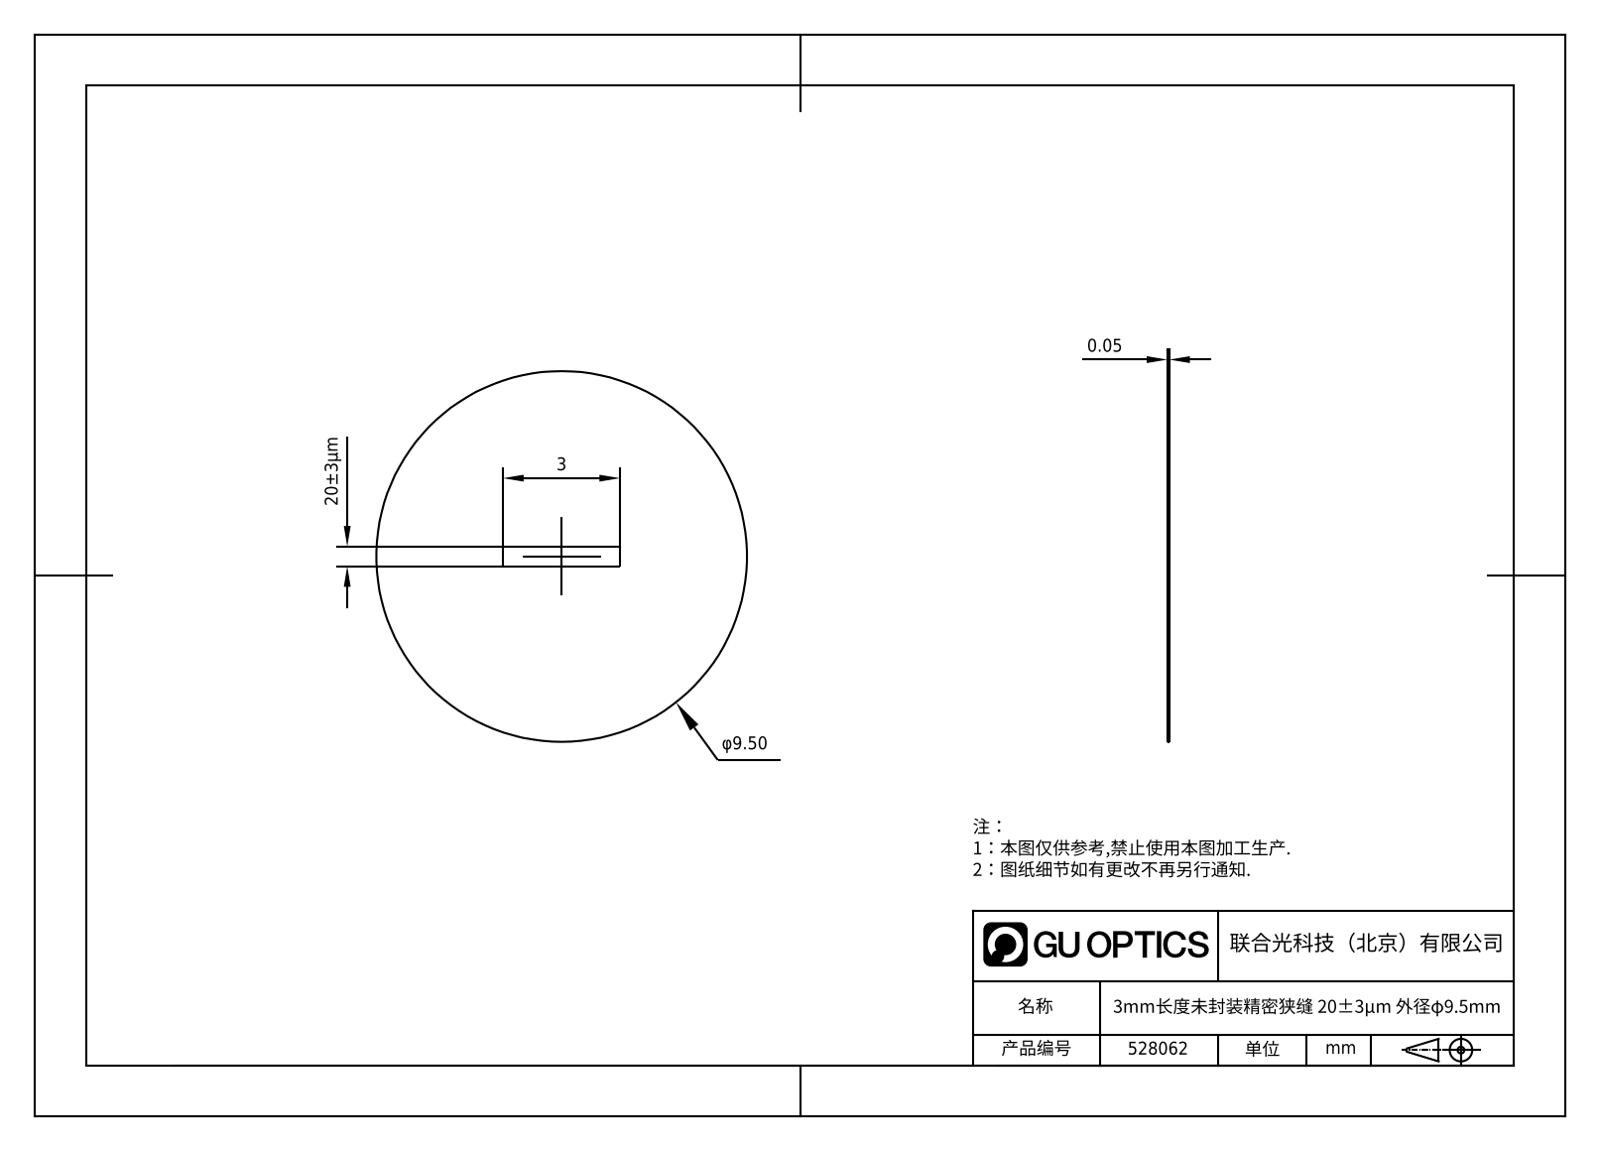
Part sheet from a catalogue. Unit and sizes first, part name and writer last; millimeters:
Units: millimetres
Overall size (bounding box): 9.5 × 9.5 × 0.05
Round bosses / shafts (diameter × count): ⌀9.5 ×1
Main face-to-face distances: 3
Volume: 4 mm³ · Surface area: 143 mm²
Bodies: 1 solid, 8 faces (6 planar, 2 cylindrical, 0 other)
Part name (STEP PRODUCT): 1.5.4.3-ZXG-9.5-20
STEP written by: SolidWorks 2021 (CONFIG_CONTROL_DESIGN)
